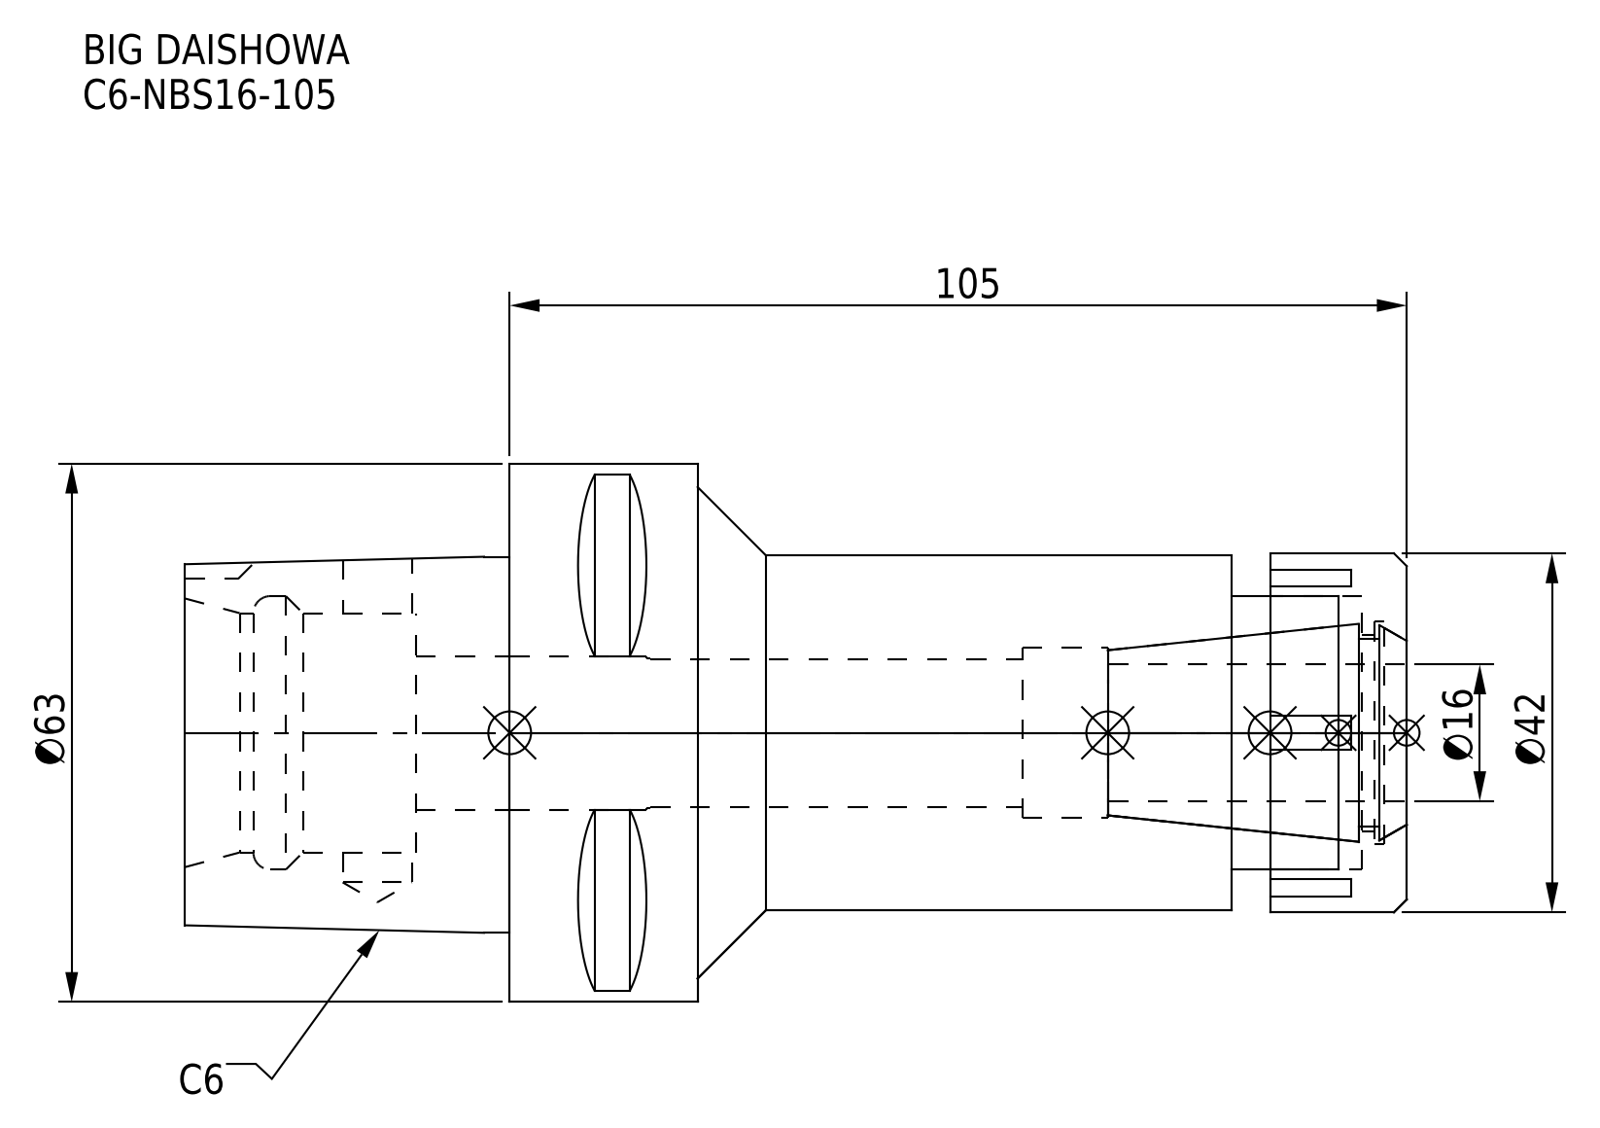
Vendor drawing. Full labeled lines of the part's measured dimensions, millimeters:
Part name (STEP PRODUCT): NBN16_1.stp; C6-NBS16-105_1.stp; DXF_TEMP_ASSY_ASM_4_ASM.stp; C6-NBS16-105-160_ASM.stp (+3 more)
STEP written by: SolidWorks 2019 (CONFIG_CONTROL_DESIGN)
Units: millimetres
Bodies: 2 solids, 112 faces (61 planar, 33 cylindrical, 18 other)
Overall size (bounding box): 143 × 63 × 63
Volume: 182 400 mm³ · Surface area: 39 238 mm²
Round holes (diameter × count): ⌀8.1 ×1, ⌀17.3 ×1, ⌀17.5 ×1, ⌀18 ×1, ⌀20 ×1, ⌀23 ×1, ⌀26 ×1, ⌀28 ×1, ⌀32 ×1
Round bosses / shafts (diameter × count): ⌀63 ×1, ⌀42 ×1, ⌀41.5 ×1
Partial cylindrical surfaces — rounded edges, fillets, slot ends (radius × count): R5 ×1
Main face-to-face distances: 105, 8, 38, 60, 20.5, 84.5, 16, 89, 4.5, 83
